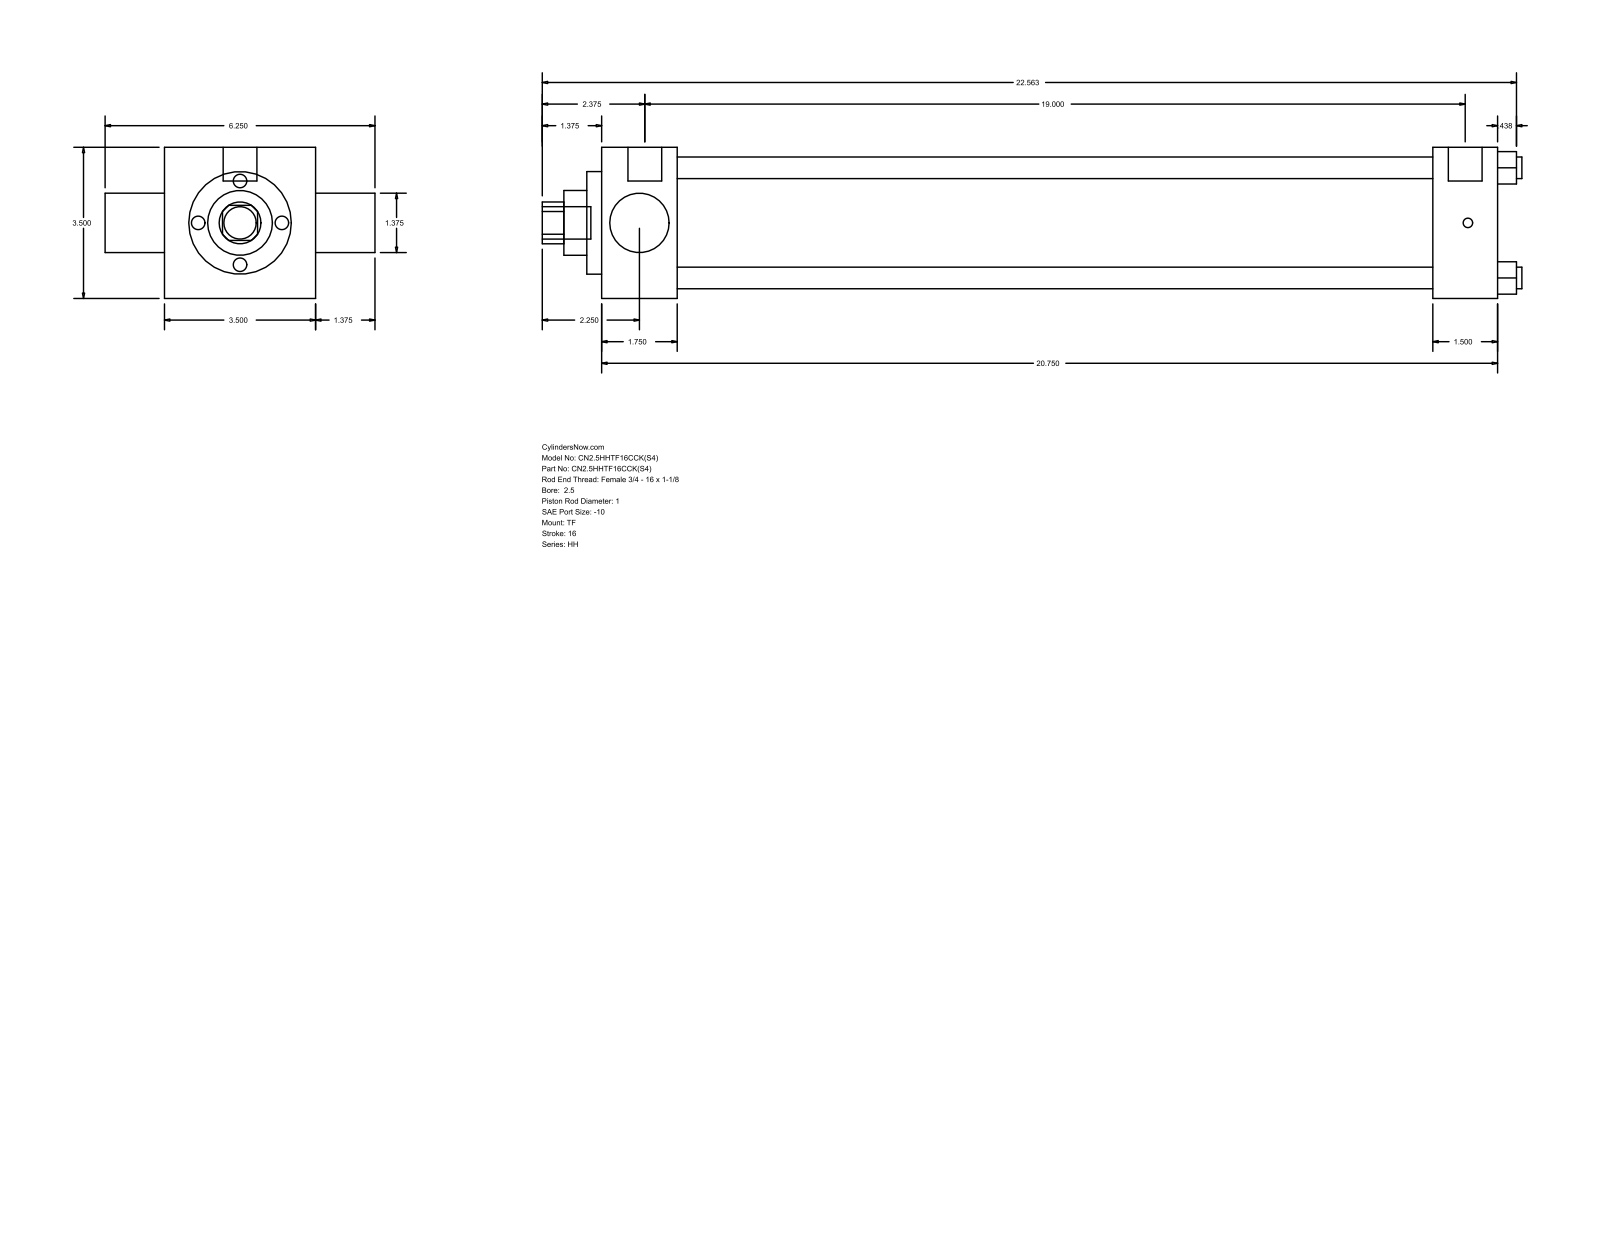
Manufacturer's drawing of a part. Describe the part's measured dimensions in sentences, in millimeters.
The part is named "HH_TF__0250_1". Its 3-D file was written by "GSSL Pune (CONFIG_CONTROL_DESIGN)". It is 0 solids with 86 faces: 61 planar, 25 cylindrical and 0 other. Overall it measures 576.26 by 158.75 by 88.9 millimeters. Round holes: 4 of diameter 12.7, 1 of diameter 25.4, 1 of diameter 34.92, 1 of diameter 38.1, 1 of diameter 60.33, 1 of diameter 73.03. Round bosses or shafts: 3 of diameter 5.56, 2 of diameter 19.84, 1 of diameter 19.05. Partial cylindrical surfaces (rounded edges, fillets, slot ends): 1 of radius 12.29. The main face-to-face distances are 88.9, 527.06, 44.46, 482.6, 488.96, 444.5, 38.1, 34.93, 123.83, 8.73. The hole center spacings are 45.79, 64.76, 91.58.
